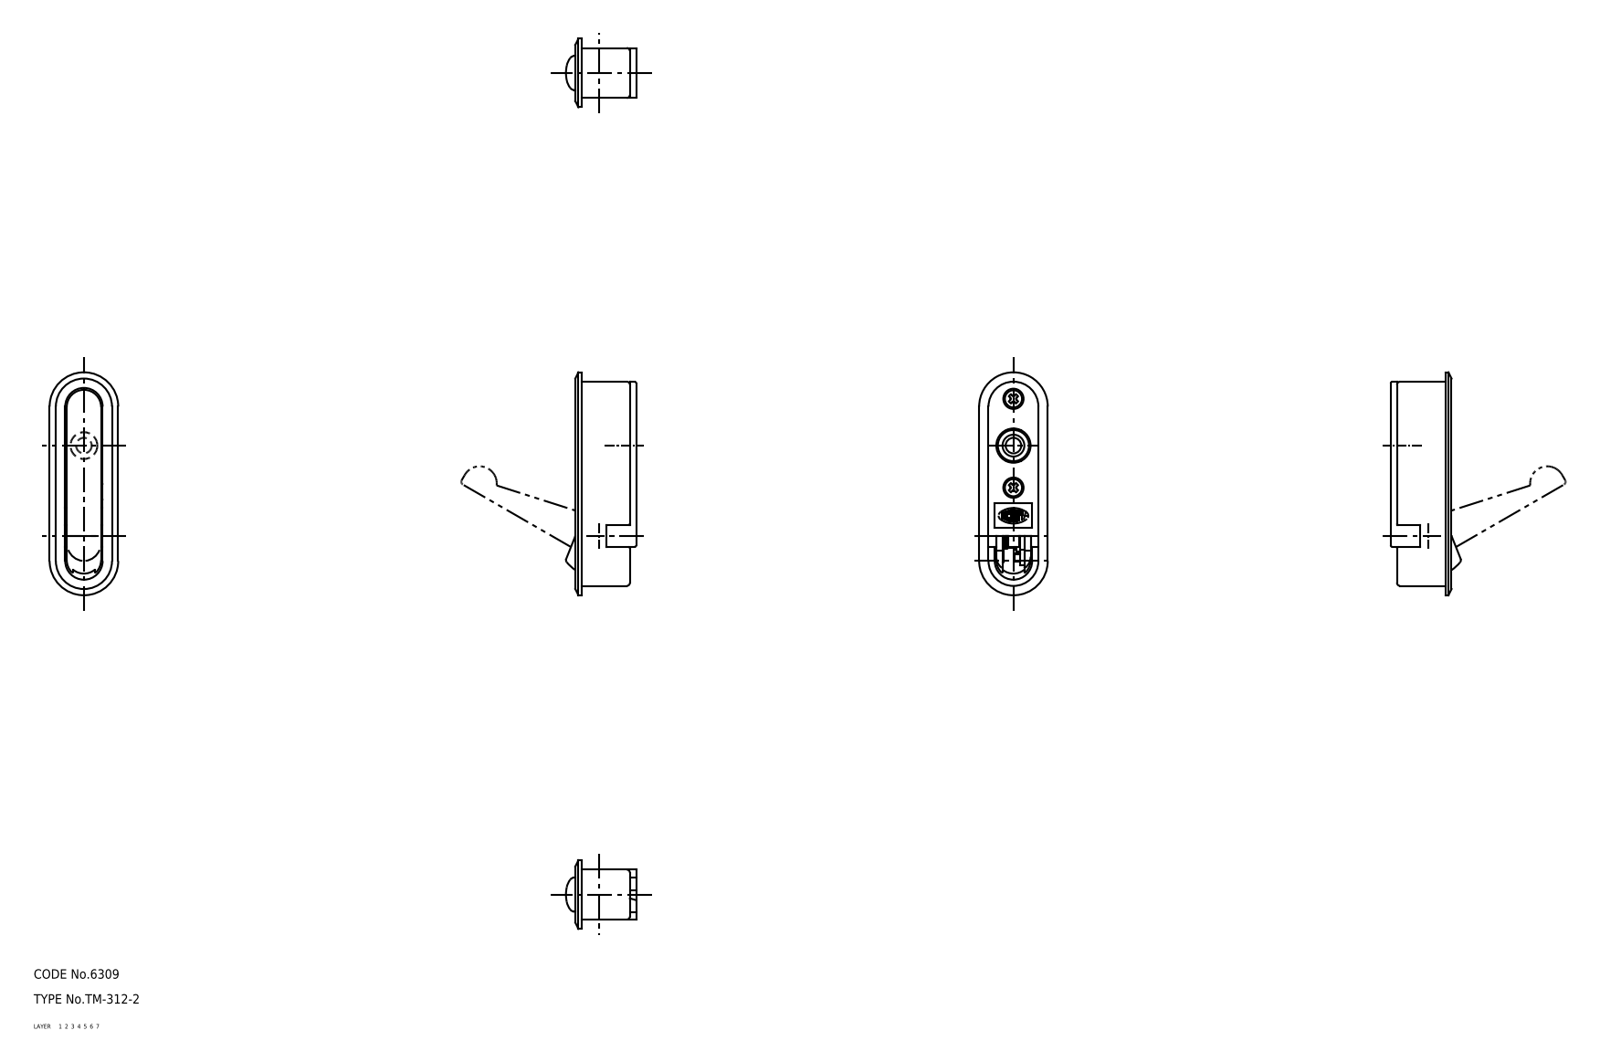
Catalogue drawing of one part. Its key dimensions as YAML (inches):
part_name: "67120098; 67120111"
step_written_by: "CADfix (AUTOMOTIVE_DESIGN)"
units: inches
bodies: {solids: 2, faces: 232, planar: 0, cylindrical: 0, other: 232}
overall_size: [2.815, 0.886, 0.866]
volume: 0.923
surface_area: 17.63
